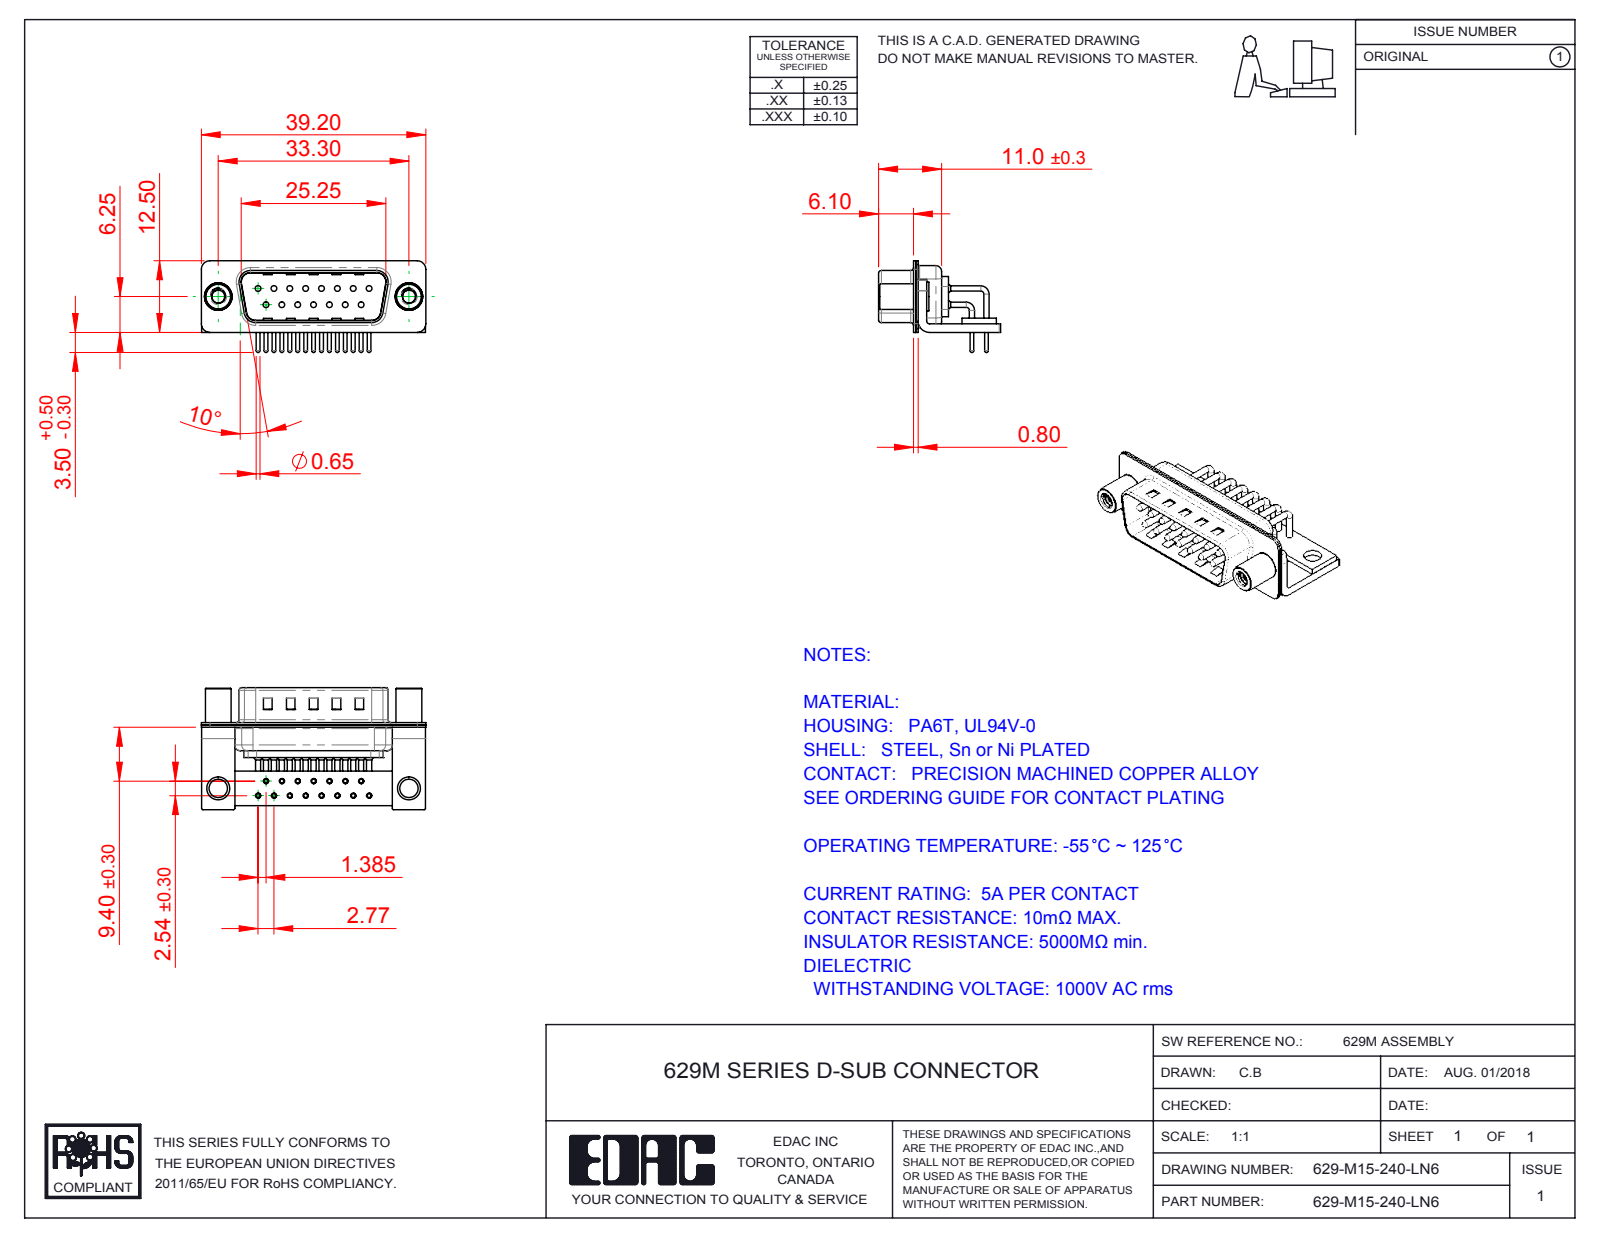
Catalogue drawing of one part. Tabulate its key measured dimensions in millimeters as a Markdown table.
| quantity | value |
| --- | --- |
| part name | 629M Contact Row 1; 629M Stabilizer Board_15 Contacts; 629M Shell Front_15 Contacts; 629M Contact Row 2 (+5 more) |
| STEP written by | SolidWorks 2016 (CONFIG_CONTROL_DESIGN) |
| units | millimeters |
| bodies | 23 solids, 2120 faces (1127 planar, 767 cylindrical, 226 other) |
| overall size | 39.2 × 21.3 × 16 |
| volume | 2 563 mm³ |
| surface area | 6 845 mm² |
| round holes (diameter × count) | 0.9 × 15, 1 × 15, 1.7 × 15, 2 × 15, 2.26 × 2, 3.2 × 2, 4 × 2, 4.8 × 2 |
| round bosses / shafts (diameter × count) | 0.9 × 21, 1.5 × 15, 0.65 × 15, 5 × 2, 4.9 × 2, 4.5 × 2 |
| partial cylindrical surfaces (radius × count) | 0.25 × 16, 1.5 × 16, 1.01 × 15, 2 × 13, 0.5 × 9, 1.6 × 8, 0.6 × 4, 0.65 × 4 |
| main face-to-face distances | 0.4, 1.5, 0.85, 0.8, 1.25, 10.4, 9.55, 1.9, 1, 8.3 |
| hole center spacings | 2.77, 5.54, 3.16, 8.31, 4.87, 11.08, 2.89, 7.37 |
